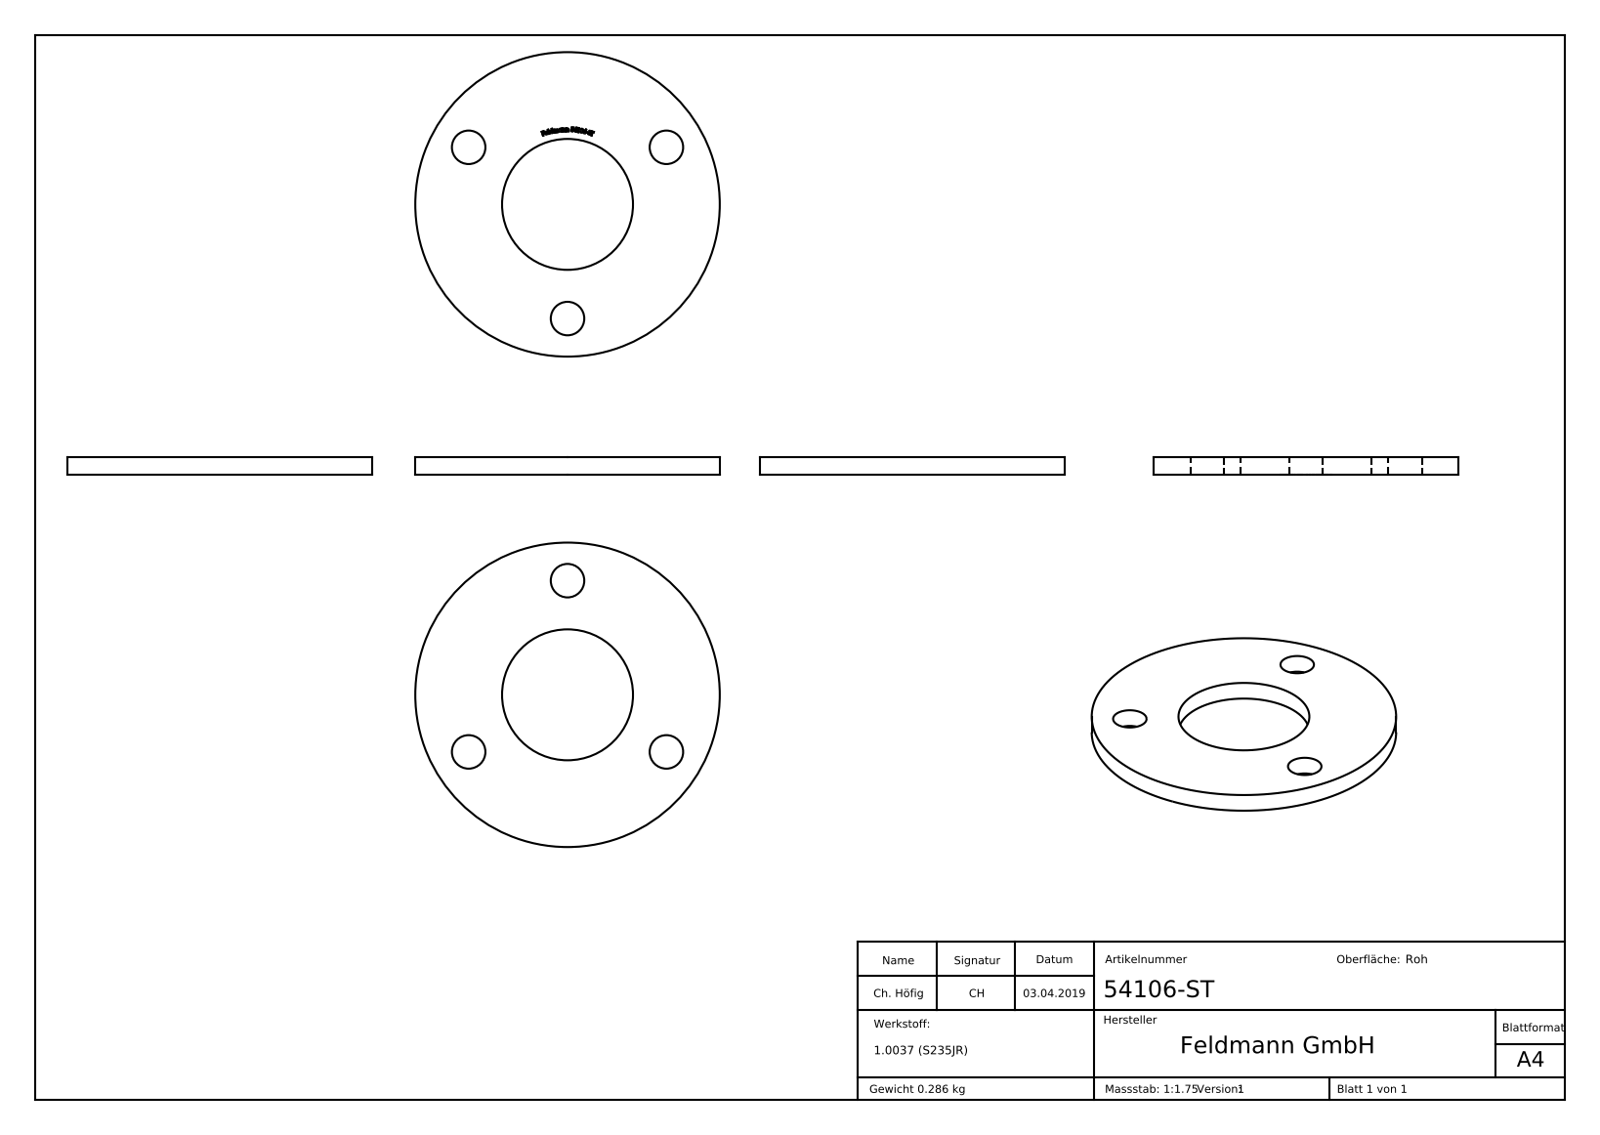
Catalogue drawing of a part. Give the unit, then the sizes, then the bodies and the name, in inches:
Units: inches
Overall size (bounding box): 3.937 × 3.937 × 0.236
Round holes (diameter × count): ⌀0.433 ×3, ⌀1.693 ×1
Round bosses / shafts (diameter × count): ⌀3.937 ×1
Main face-to-face distances: 0.236, 0.232, 0.021, 0.033, 0.052, 0.029, 0.028, 0.024, 0.057, 0.026
Hole centre spacings: 1.476, 2.557, 2.557
Volume: 2.24 in³ · Surface area: 24.12 in²
Bodies: 1 solid, 219 faces (120 planar, 10 cylindrical, 89 other)
Part name (STEP PRODUCT): 54106-ST
STEP written by: SolidWorks 2015 (CONFIG_CONTROL_DESIGN)
